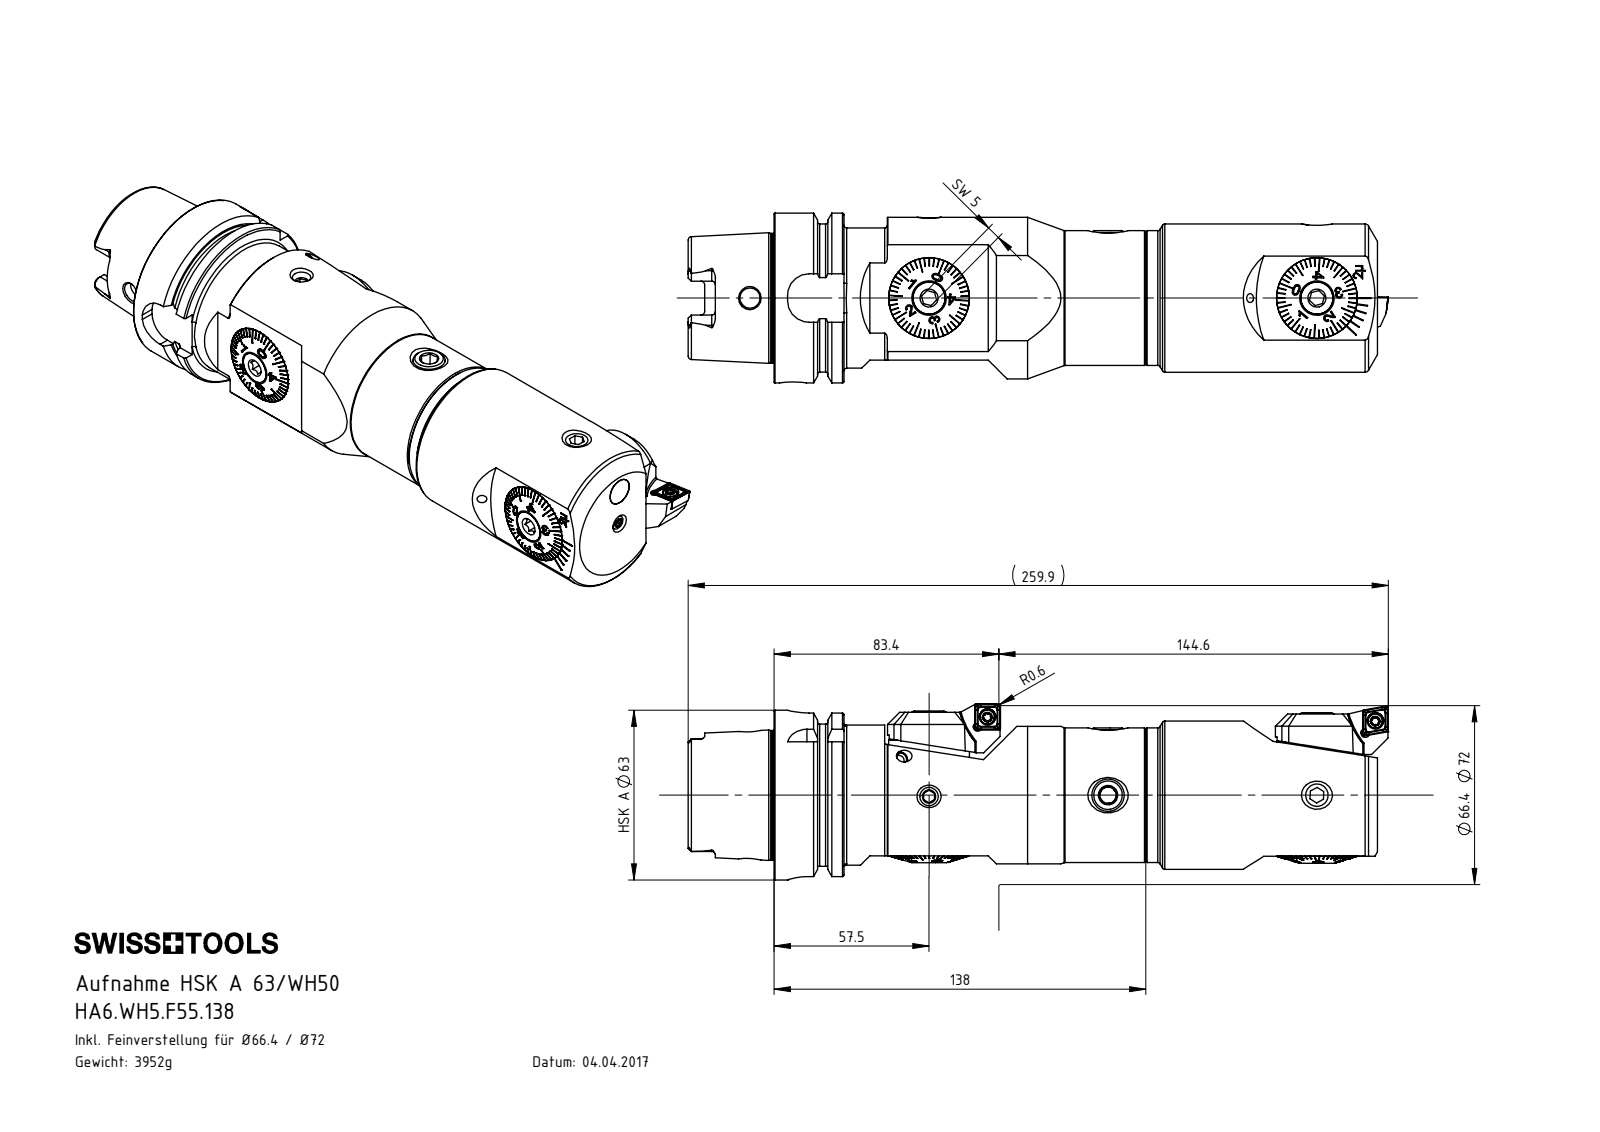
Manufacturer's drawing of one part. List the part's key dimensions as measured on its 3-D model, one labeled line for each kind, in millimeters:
Part name (STEP PRODUCT): F55-WCB.001.013; F55-BG1.So1.036_F55 Min Max; CCMT09T304; DIN 3771 - 25x1.5 (+8 more)
STEP written by: SolidWorks 2017 (CONFIG_CONTROL_DESIGN)
Units: millimetres
Bodies: 42 solids, 2033 faces (762 planar, 419 cylindrical, 852 other)
Overall size (bounding box): 259.9 × 65.3 × 63
Volume: 491 094 mm³ · Surface area: 122 193 mm²
Round holes (diameter × count): ⌀3.3 ×14, ⌀4.2 ×4, ⌀5 ×4, ⌀8.5 ×4, ⌀11 ×4, ⌀10 ×3, ⌀17 ×3, ⌀4 ×2, ⌀4.4 ×2, ⌀6 ×2, ⌀6.1 ×2, ⌀8 ×2
Round bosses / shafts (diameter × count): ⌀5.25 ×4, ⌀4 ×4, ⌀10 ×3, ⌀29.98 ×2, ⌀29.9 ×2, ⌀25 ×2, ⌀18 ×2, ⌀16 ×2
Partial cylindrical surfaces — rounded edges, fillets, slot ends (radius × count): R0.34 ×24, R0.59 ×24, R0.5 ×8, R1.4 ×6, R3.2 ×6, R2.88 ×4, R8 ×4, R10 ×4
Main face-to-face distances: 0.65, 40, 86, 23.5, 138, 224, 2.5, 2.6, 3.25, 10
Hole centre spacings: 14.5, 66.45, 77.55, 143.92, 144, 144.01, 1.88, 5.06
